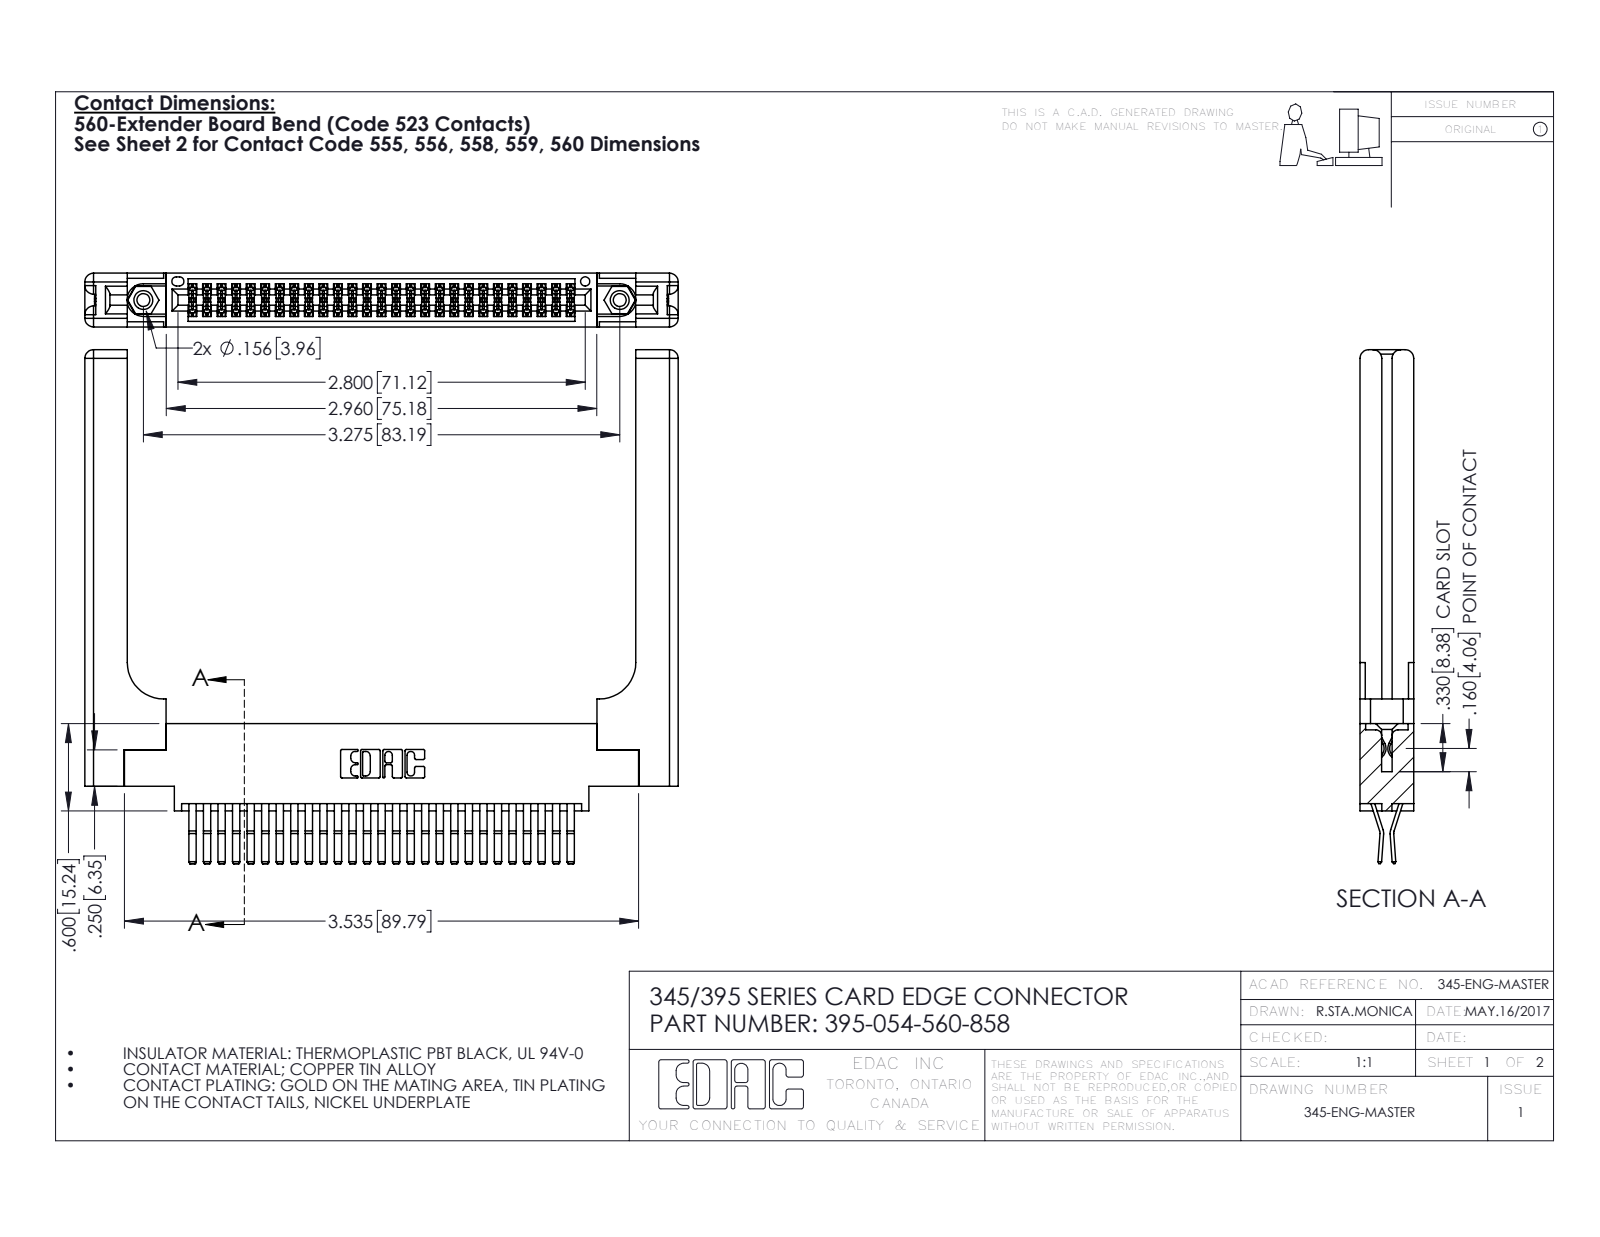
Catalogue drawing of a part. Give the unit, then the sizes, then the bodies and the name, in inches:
Units: inches
Overall size (bounding box): 4.079 × 3.532 × 0.37
Round holes (diameter × count): ⌀0.089 ×2, ⌀0.125 ×2, ⌀0.156 ×2, ⌀0.064 ×1
Round bosses / shafts (diameter × count): ⌀0.155 ×2
Partial cylindrical surfaces — rounded edges, fillets, slot ends (radius × count): R0.006 ×81, R0.01 ×22, R0.06 ×16, R0.007 ×6, R0.031 ×6, R0.026 ×3, R0.01 ×2, R0.014 ×2
Main face-to-face distances: 0.37, 0.072, 0.298, 0.025, 0.225, 0.148, 0.15, 0.098, 0.272, 0.2
Hole centre spacings: 0.27, 3.04, 3.275
Volume: 1.138 in³ · Surface area: 32.32 in²
Bodies: 59 solids, 3194 faces (2014 planar, 1120 cylindrical, 60 other)
Part name (STEP PRODUCT): 395-054-560-858; 345-220-058_345-220-058; 345-292-001_560 Tail; 345-250-001_345-250-001-102 (+1 more)
STEP written by: SolidWorks 2016 (CONFIG_CONTROL_DESIGN)
